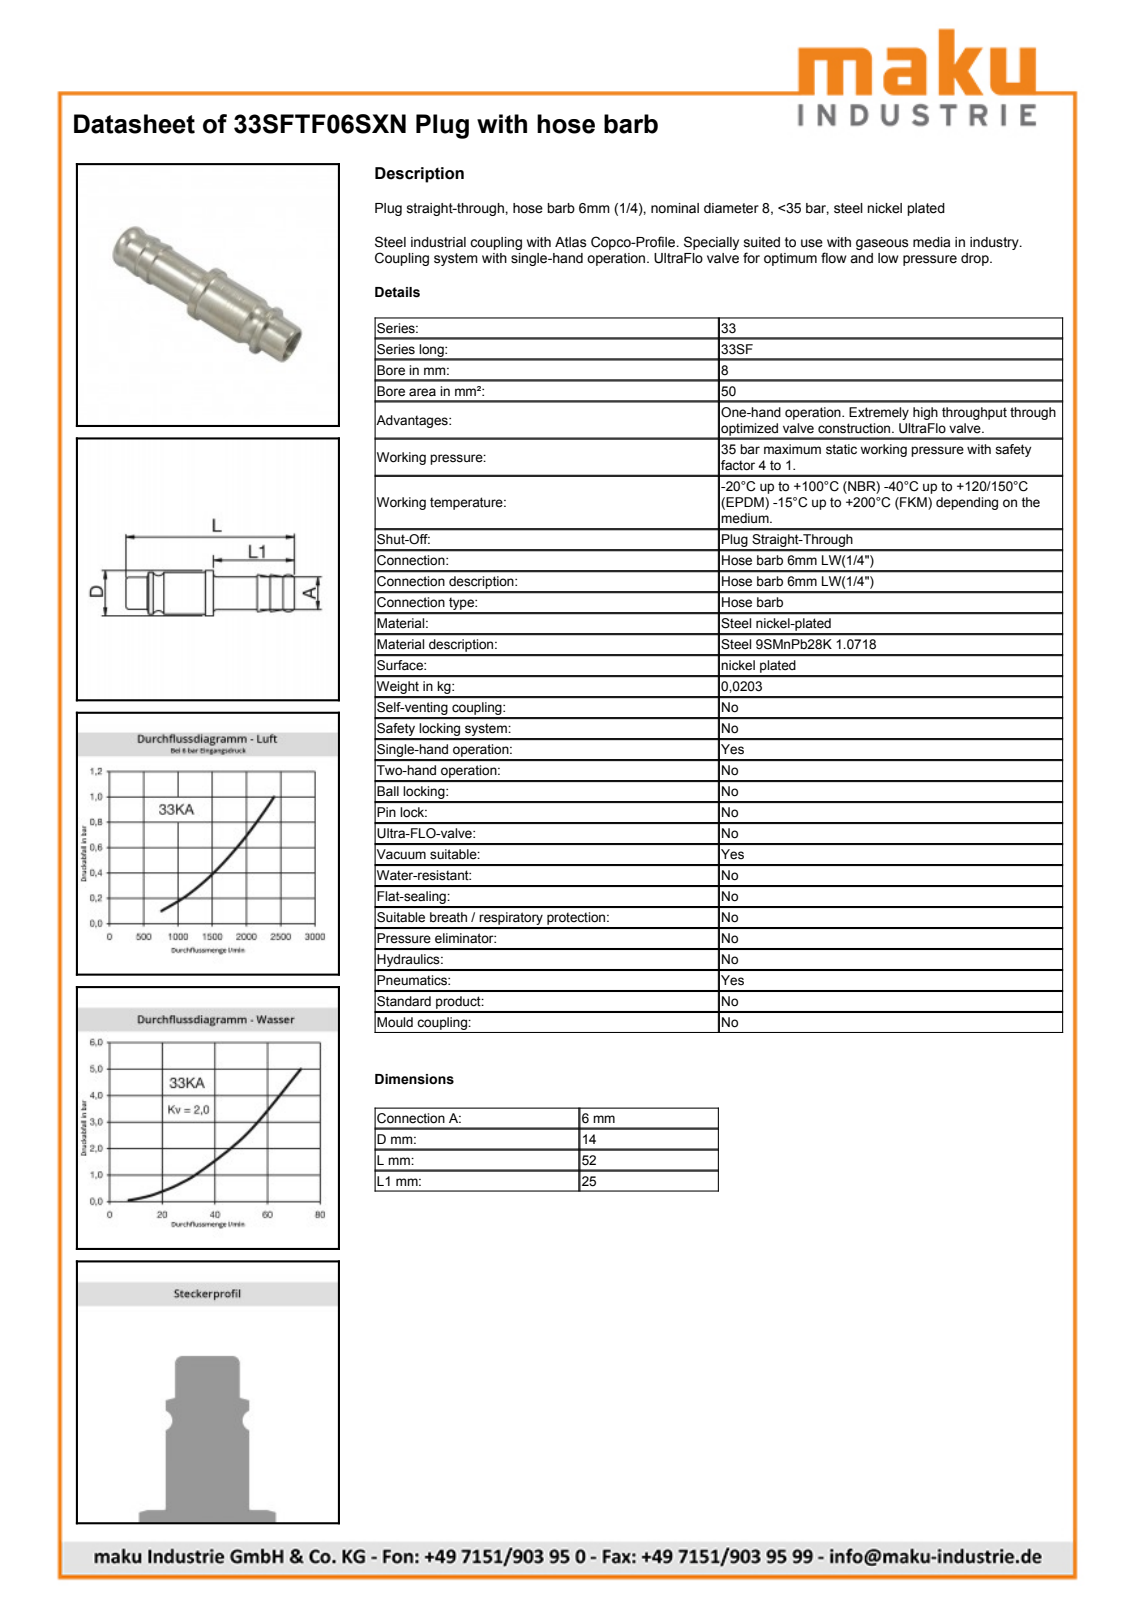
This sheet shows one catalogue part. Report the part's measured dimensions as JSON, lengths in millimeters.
{"part_name": "D107392", "step_written_by": "Autodesk Inventor 2013 (AUTOMOTIVE_DESIGN)", "units": "millimeters", "bodies": {"solids": 1, "faces": 25, "planar": 6, "cylindrical": 7, "other": 12}, "overall_size": [52, 14, 14], "volume_mm3": 2618, "surface_area_mm2": 2716, "round_holes": [[4.1, 1], [7, 1]], "round_bosses_or_shafts": [[14, 1], [12.9, 1], [9.9, 1], [6.1, 1]], "face_to_face_distances": [25, 52, 27, 11.5, 13.5, 40.5, 27.5, 16, 2.5, 24.5]}
